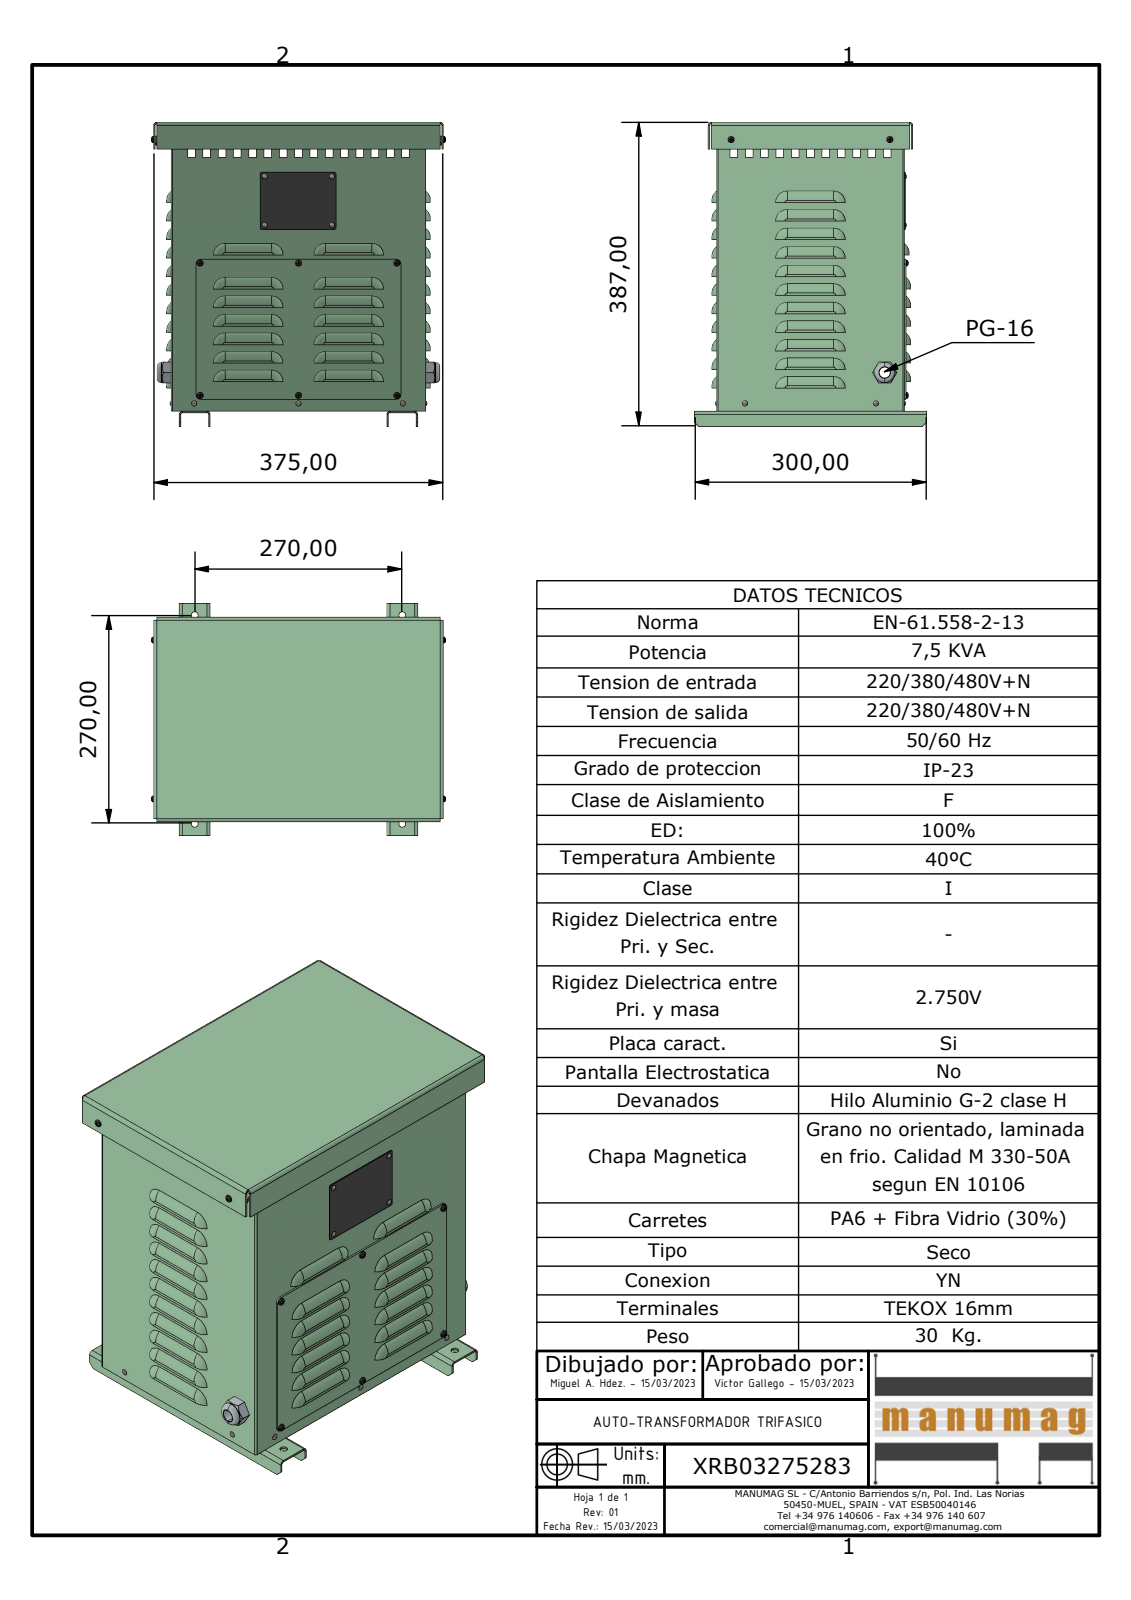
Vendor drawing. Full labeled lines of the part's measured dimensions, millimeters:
Part name (STEP PRODUCT): XRB03275283; JE010 EXPORT BASE; JE010 EXPORT PATA; JE010 EXPORT CUERPO (+6 more)
STEP written by: Autodesk Inventor 2023 (AUTOMOTIVE_DESIGN)
Units: millimetres
Bodies: 33 solids, 1975 faces (1082 planar, 421 cylindrical, 472 other)
Overall size (bounding box): 394.02 × 381.14 × 300
Volume: 1 720 000 mm³ · Surface area: 1 517 000 mm²
Round holes (diameter × count): ⌀2.3 ×8, ⌀3.7 ×8, ⌀8.8 ×8, ⌀4.3 ×5, ⌀3.4 ×4, ⌀4 ×4, ⌀5 ×3, ⌀14 ×1, ⌀24 ×1
Round bosses / shafts (diameter × count): ⌀3.2 ×9, ⌀4 ×8, ⌀3.62 ×8, ⌀26 ×1, ⌀23 ×1, ⌀22.5 ×1
Partial cylindrical surfaces — rounded edges, fillets, slot ends (radius × count): R14 ×105, R4 ×68, R15 ×40, R2 ×20, R1.5 ×6, R2 ×5, R6 ×4
Main face-to-face distances: 2, 240.62, 327.32, 372.01, 242.62, 374.01, 238.62, 325.32, 329.32, 4
Hole centre spacings: 55.99, 127.3, 168.89, 210.03, 213.21, 213.3, 342.86, 62.98
